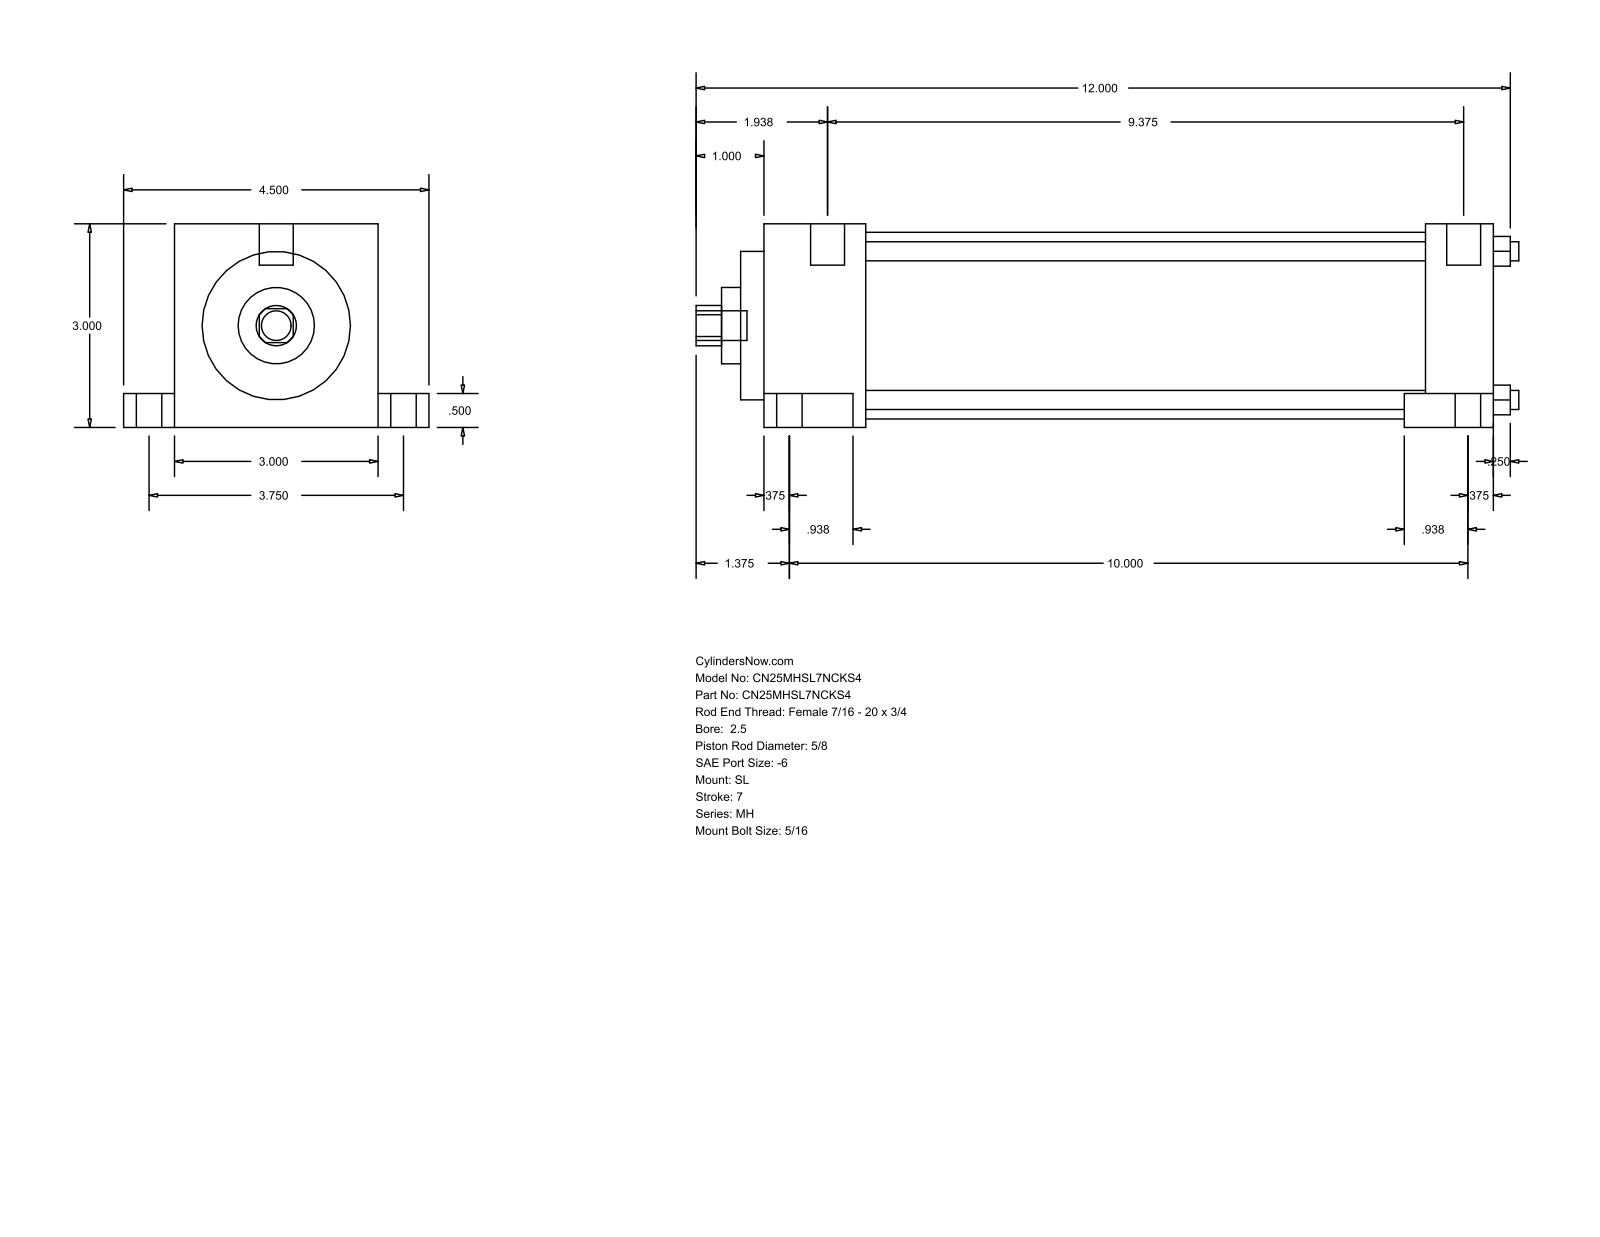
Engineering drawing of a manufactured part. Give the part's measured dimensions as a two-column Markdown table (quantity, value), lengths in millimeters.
| quantity | value |
| --- | --- |
| part name | MH_SL__0250_0.625 |
| STEP written by | GSSL Pune (CONFIG_CONTROL_DESIGN) |
| units | millimeters |
| bodies | 0 solids, 86 faces (61 planar, 25 cylindrical, 0 other) |
| overall size | 307.98 × 114.3 × 76.2 |
| round holes (diameter × count) | 7.14 × 4, 15.88 × 1, 28.57 × 1, 55.55 × 1, 69.85 × 1 |
| round bosses / shafts (diameter × count) | 15.88 × 2, 9.53 × 2, 5.56 × 2, 12.7 × 1, 11.11 × 1 |
| partial cylindrical surfaces (radius × count) | 7.54 × 1 |
| main face-to-face distances | 76.2, 25.4, 256.38, 281.78, 12.7, 63.5, 19.05, 95.25, 31.75, 248.44 |
| hole center spacings | 39.33, 55.62, 78.66 |
